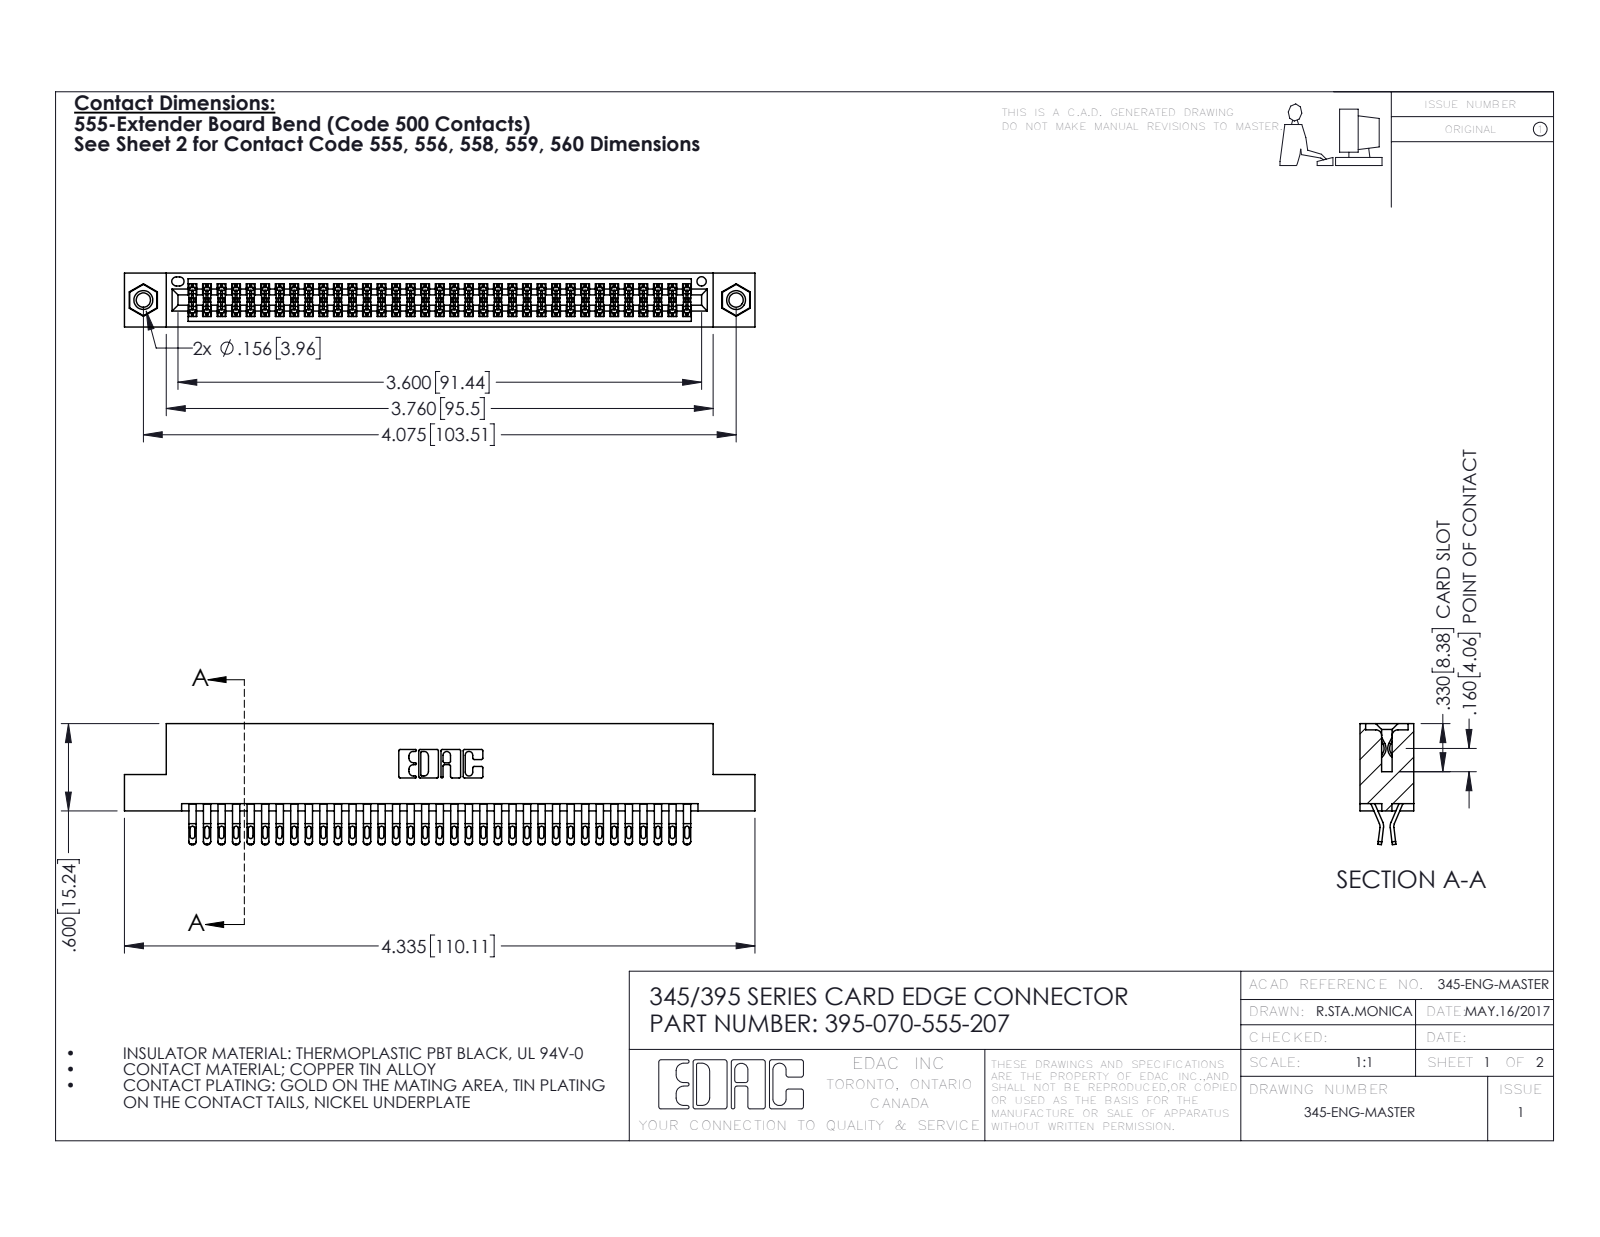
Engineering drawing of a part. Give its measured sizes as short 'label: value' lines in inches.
name: 395-070-555-207; 345-292-001_555 Tail; 345-250-001_345-250-005-103; 345 Part_Flush Mounting Lugs - 0.156 Dia-TI
written by: SolidWorks 2016 (CONFIG_CONTROL_DESIGN)
unit: in
bodies: 73 solids, 4106 faces (2282 planar, 1808 cylindrical, 16 other)
size: 4.335 × 0.832 × 0.37
volume: 0.66 in³; area: 25.72 in²
holes: 2× ⌀0.098, 2× ⌀0.125, 2× ⌀0.156, 1× ⌀0.064
bosses: 2× ⌀0.155
rounds: 175× R0.016, 140× R0.02, 105× R0.006, 22× R0.01, 6× R0.007, 6× R0.031, 3× R0.026, 2× R0.01
face distances: 0.072, 0.298, 0.37, 0.025, 0.2, 0.098, 0.272, 0.225, 0.175, 0.149
hole spacings: 0.27, 3.839, 4.075
